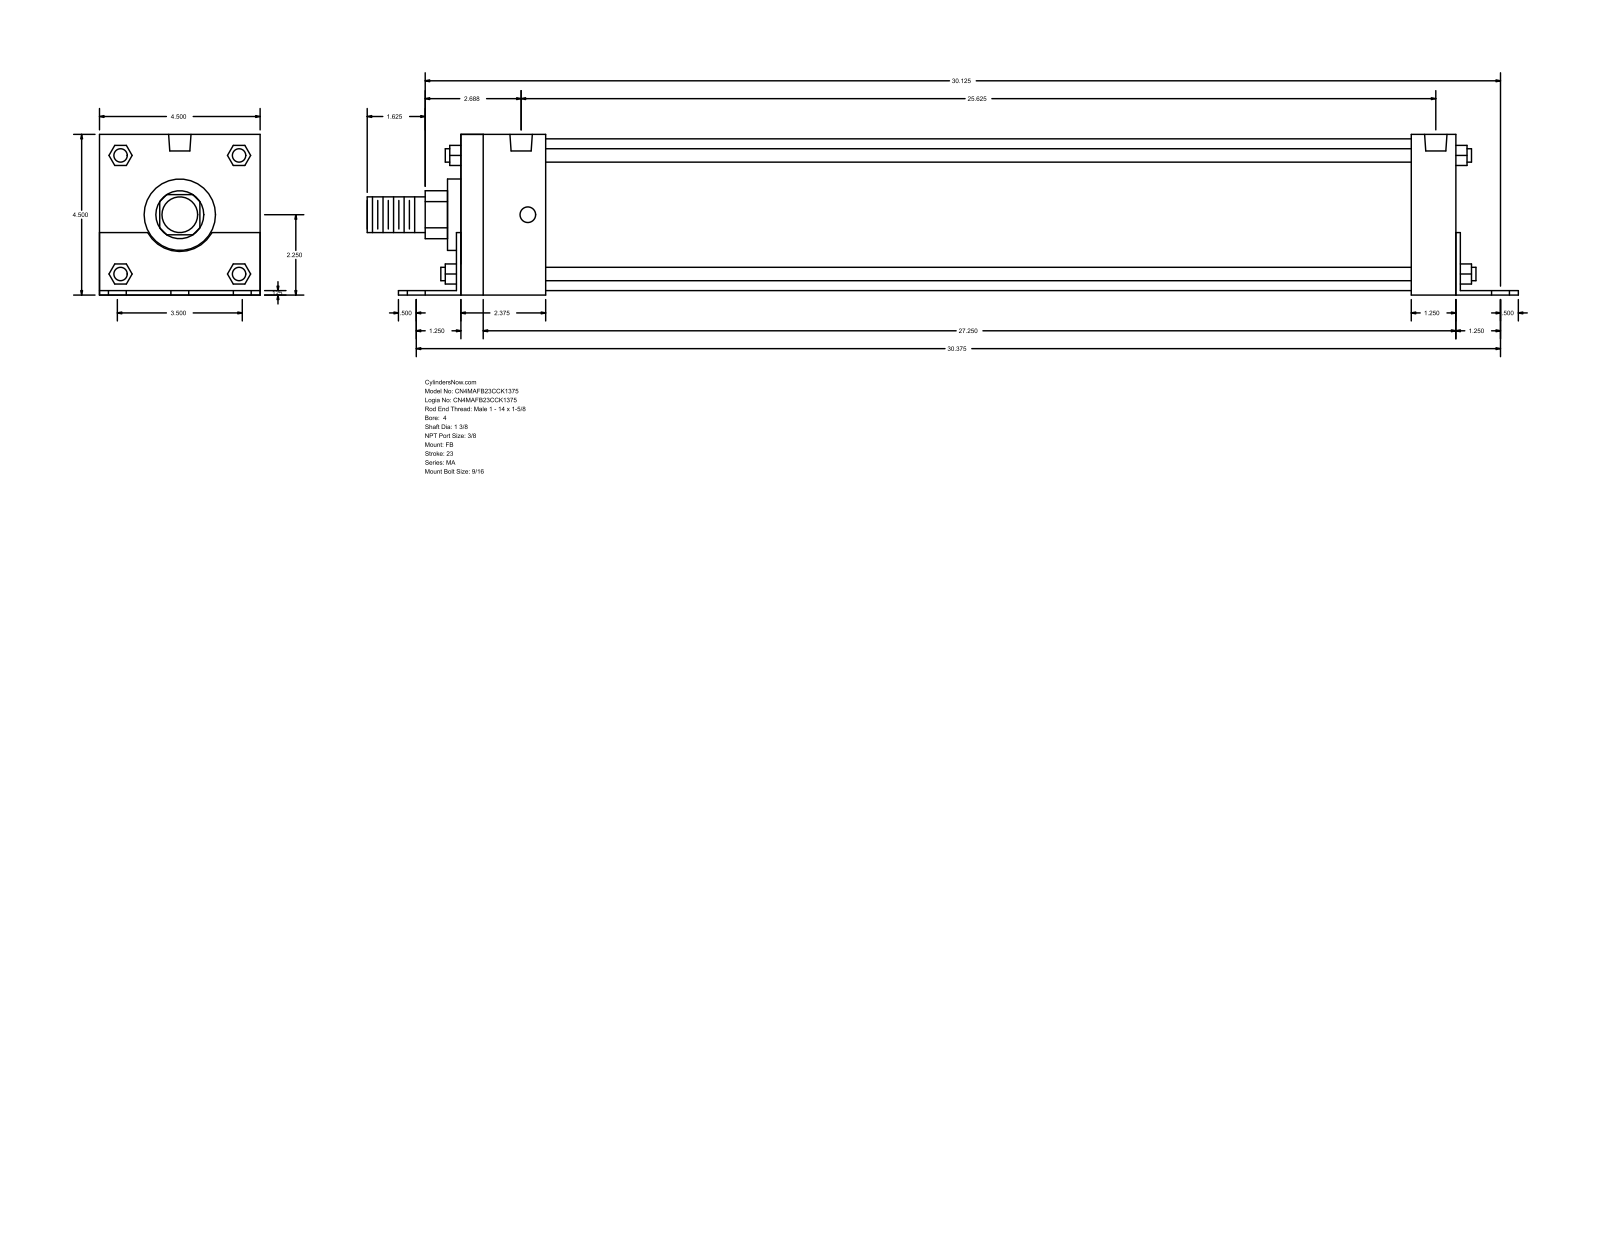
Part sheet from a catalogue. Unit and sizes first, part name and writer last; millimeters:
Units: millimetres
Overall size (bounding box): 819.15 × 114.35 × 114.3
Round holes (diameter × count): ⌀14.29 ×6, ⌀11.11 ×4, ⌀15.93 ×2
Round bosses / shafts (diameter × count): ⌀9.53 ×4, ⌀107.95 ×1, ⌀50.8 ×1, ⌀34.92 ×1, ⌀25.4 ×1
Partial cylindrical surfaces — rounded edges, fillets, slot ends (radius × count): R17.06 ×1, R26.16 ×1
Main face-to-face distances: 114.3, 3.17, 114.35, 3.12, 111.18, 708.02, 3.18, 711.2, 34.93, 711.19
Hole centre spacings: 44.45, 772.8, 771.52, 63.99, 67.49, 86.85, 88.9, 90.98
Bodies: 0 solids, 140 faces (105 planar, 35 cylindrical, 0 other)
Part name (STEP PRODUCT): MA_FB__0400_1.375
STEP written by: GSSL Pune (CONFIG_CONTROL_DESIGN)
